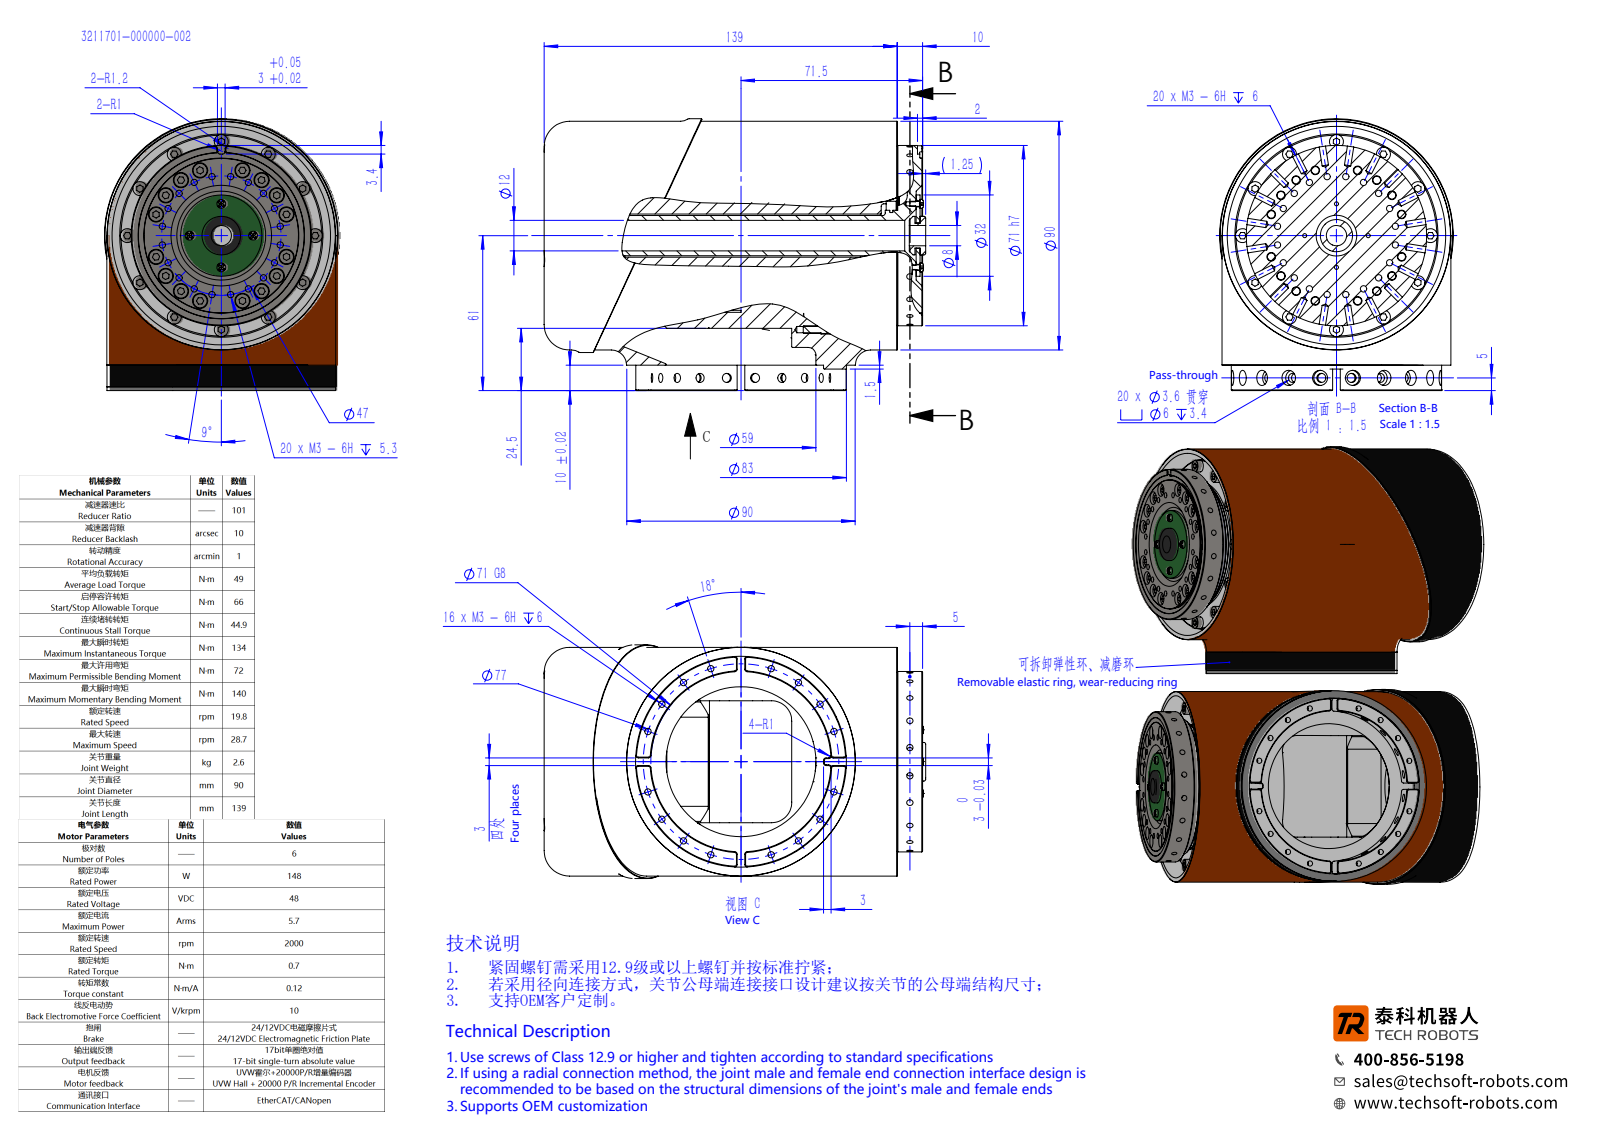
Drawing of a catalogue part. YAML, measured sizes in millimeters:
step_written_by: "SolidWorks 2016 (CONFIG_CONTROL_DESIGN)"
units: millimeters
bodies: {solids: 23, faces: 1904, planar: 658, cylindrical: 779, other: 467}
overall_size: [150.25, 107, 92]
volume: 906752
surface_area: 117605
round_holes:
  - {diameter: 2.5, count: 72}
  - {diameter: 3.5, count: 36}
  - {diameter: 6, count: 32}
  - {diameter: 3.4, count: 19}
  - {diameter: 3.6, count: 16}
  - {diameter: 1.6, count: 12}
  - {diameter: 2.4, count: 4}
  - {diameter: 7, count: 3}
  - {diameter: 8, count: 1}
  - {diameter: 10, count: 1}
  - {diameter: 12, count: 1}
  - {diameter: 18, count: 1}
round_bosses_or_shafts:
  - {diameter: 5.5, count: 32}
  - {diameter: 3, count: 32}
  - {diameter: 3.5, count: 4}
  - {diameter: 2, count: 4}
  - {diameter: 92, count: 1}
  - {diameter: 90, count: 1}
  - {diameter: 83, count: 1}
  - {diameter: 80, count: 1}
partial_cylinders:
  - {radius: 4.5, count: 40}
  - {radius: 1, count: 22}
  - {radius: 0.3, count: 4}
  - {radius: 3, count: 4}
  - {radius: 8, count: 4}
  - {radius: 0.5, count: 2}
  - {radius: 1.2, count: 2}
  - {radius: 1.7, count: 2}
face_to_face_distances: [14.5, 10, 132, 16, 71.5, 9, 7.5, 7, 67.5, 24.5]
hole_center_spacings: [23.5, 41.88, 44.7, 7.35, 27.63, 38.5, 54.45, 14.52]
